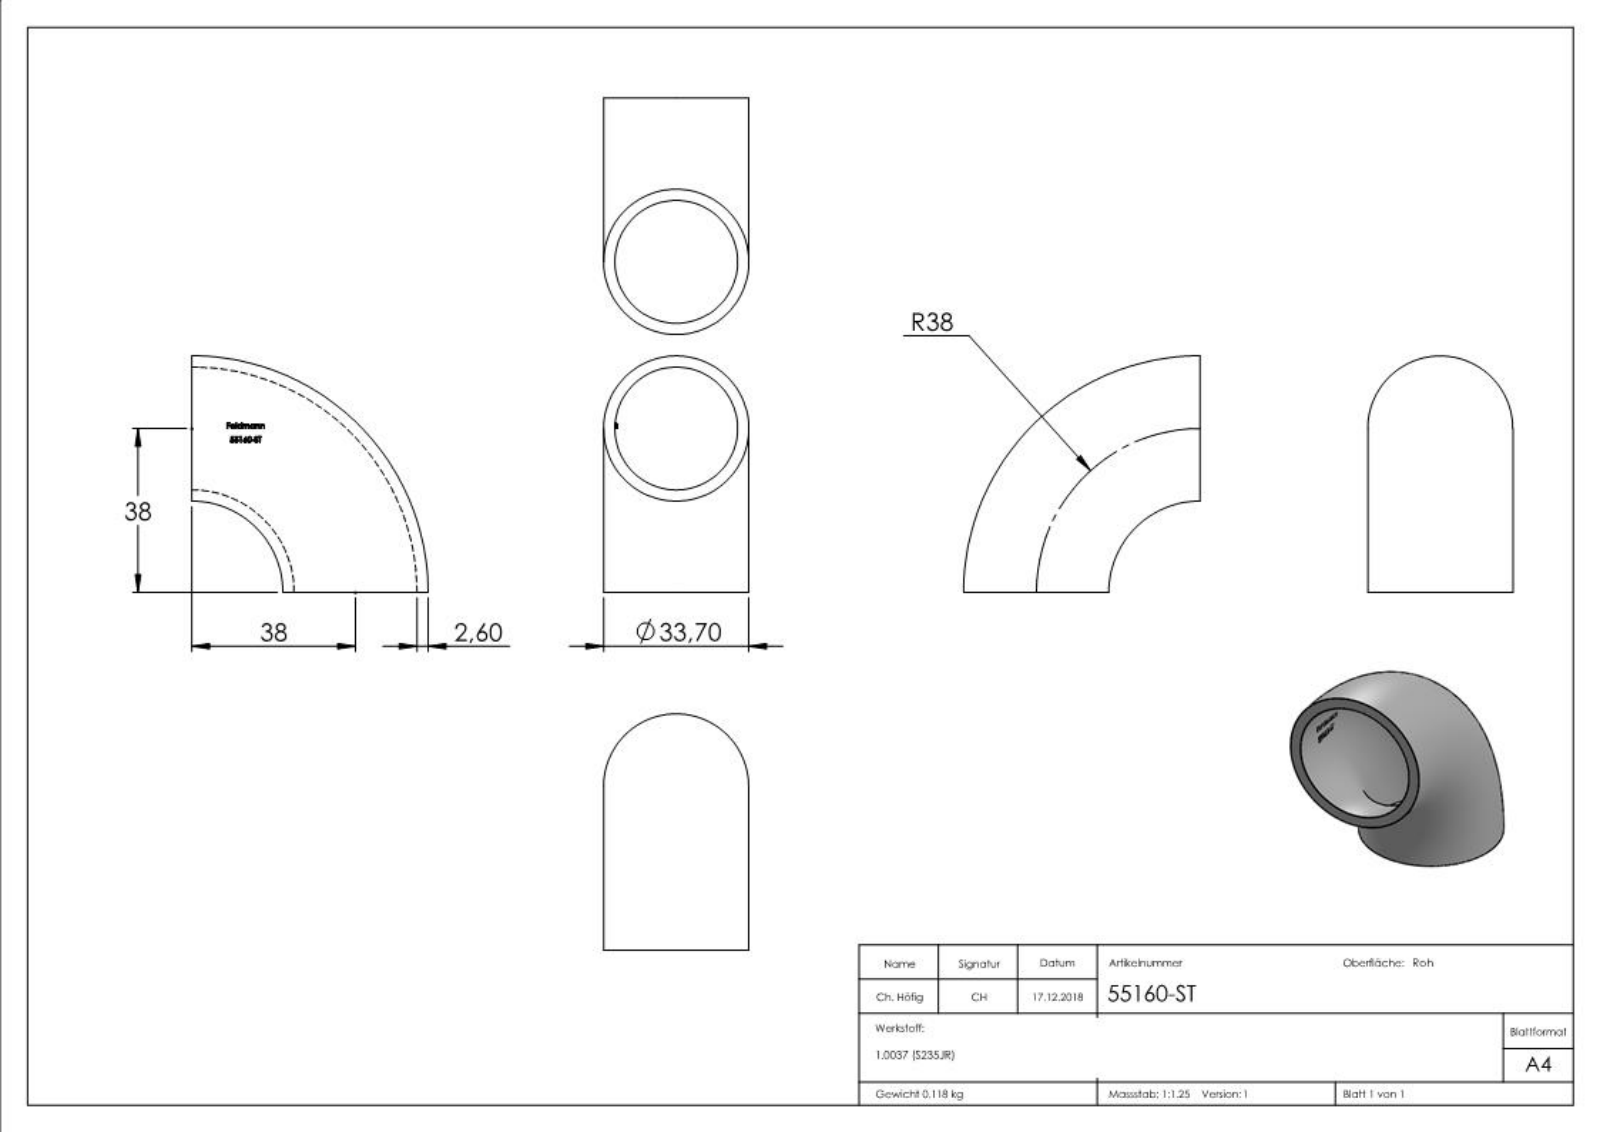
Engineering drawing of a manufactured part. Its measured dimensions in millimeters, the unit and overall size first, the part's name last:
Units: millimetres
Overall size (bounding box): 54.85 × 54.85 × 33.7
Main face-to-face distances: 2.97, 3.09, 3.27, 3.54, 2.02, 0.39, 4.43, 3.21, 3.66, 7.52
Volume: 15 163 mm³ · Surface area: 12 181 mm²
Bodies: 1 solid, 213 faces (91 planar, 0 cylindrical, 122 other)
Part name (STEP PRODUCT): 55160-ST
STEP written by: SolidWorks 2015 (CONFIG_CONTROL_DESIGN)
